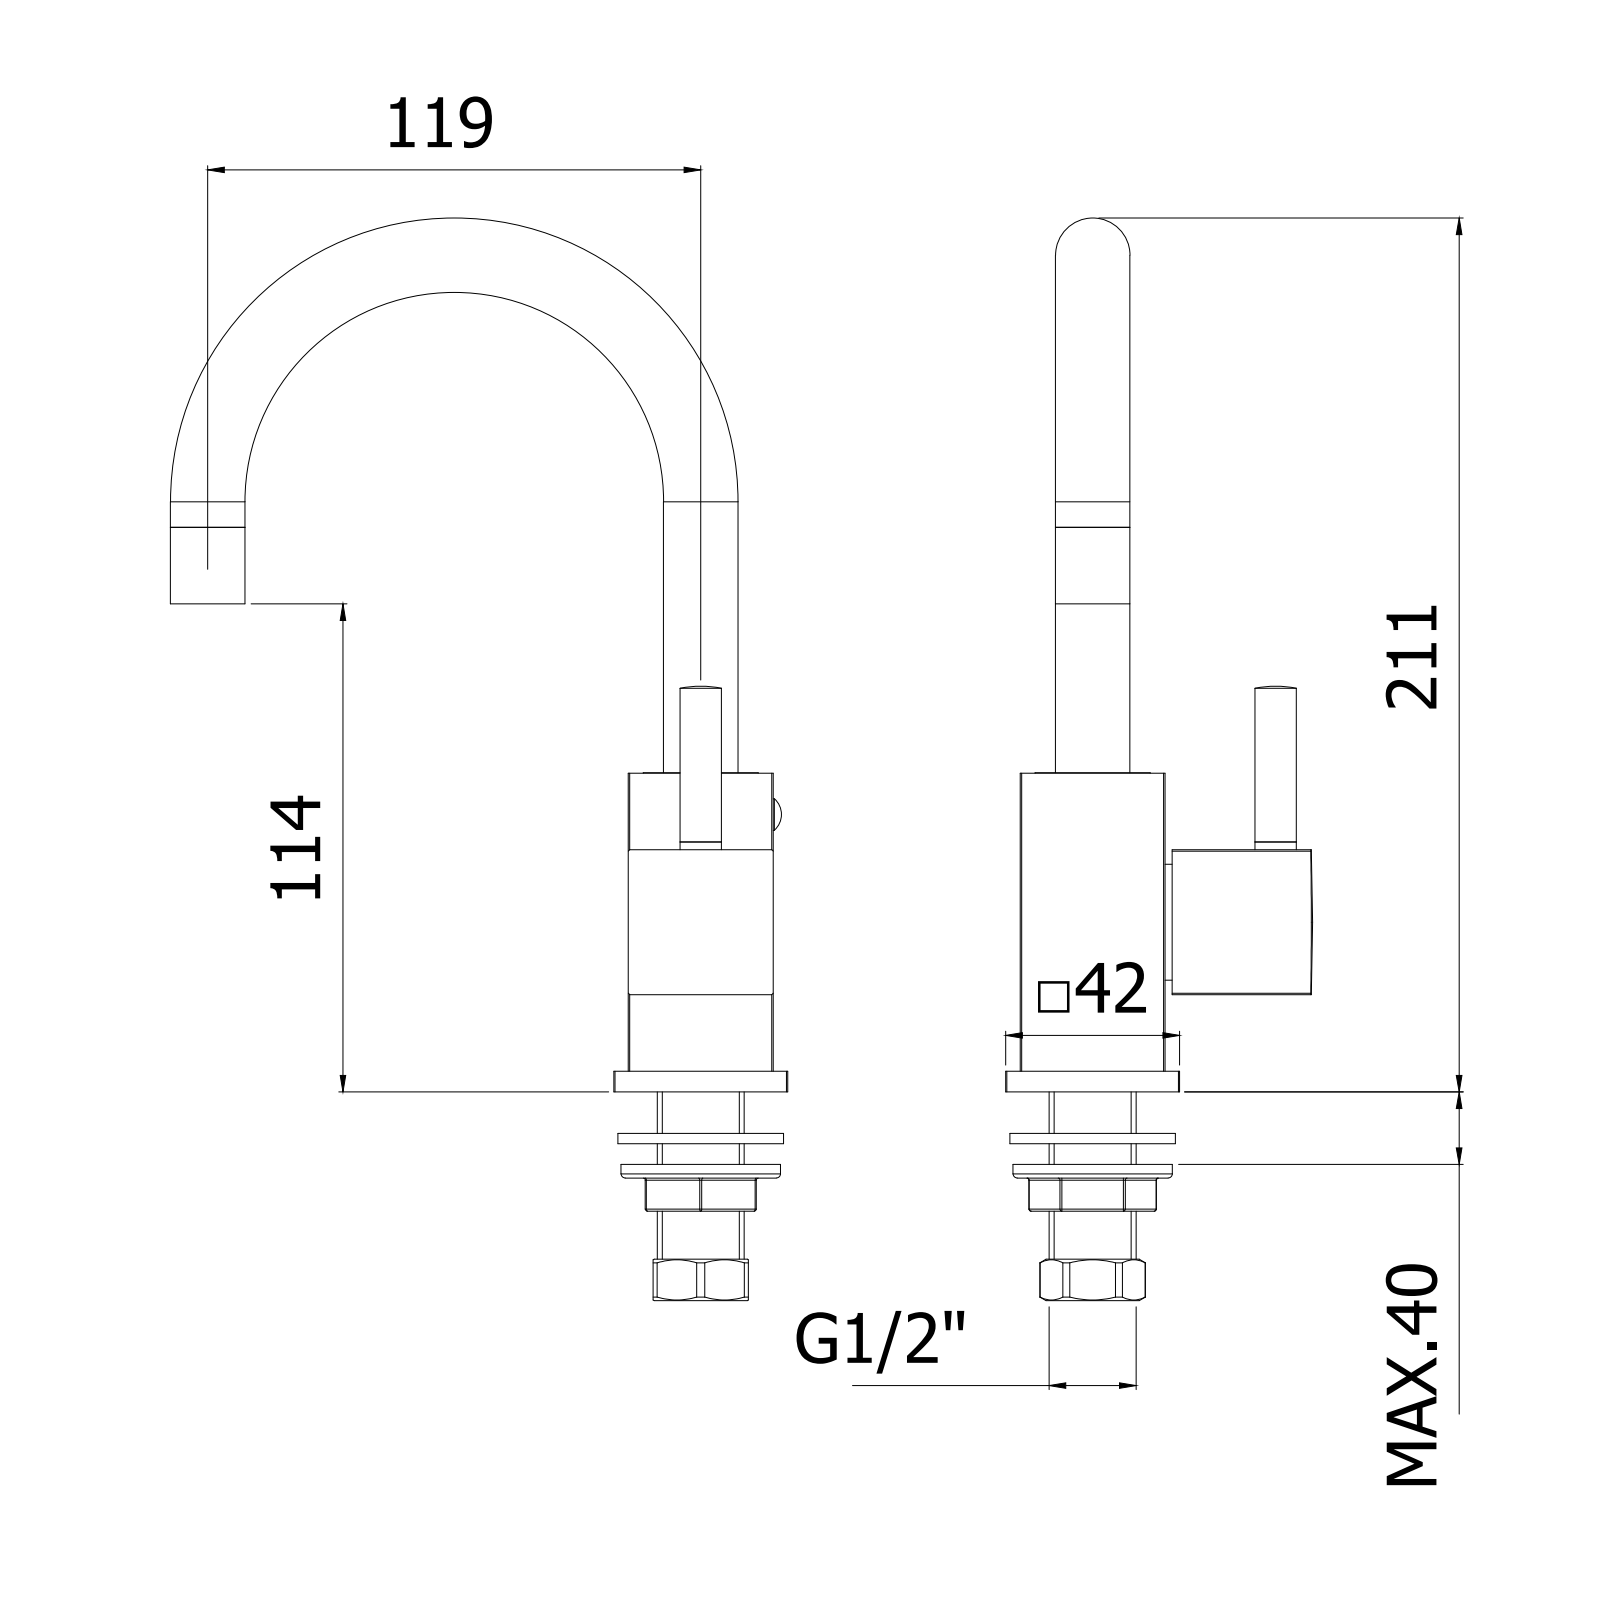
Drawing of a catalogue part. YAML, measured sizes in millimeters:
part_name: "LEA091CR"
step_written_by: "CREO PARAMETRIC BY PTC INC, 2020044 (CONFIG_CONTROL_DESIGN)"
units: millimeters
bodies: {solids: 2, faces: 508, planar: 118, cylindrical: 326, other: 64}
overall_size: [211.1, 149.1, 74.49]
volume: 145388
surface_area: 64763
round_holes:
  - {diameter: 0.5, count: 51}
  - {diameter: 6, count: 2}
  - {diameter: 15, count: 2}
  - {diameter: 22, count: 2}
  - {diameter: 3, count: 1}
  - {diameter: 4, count: 1}
  - {diameter: 4.5, count: 1}
  - {diameter: 5.5, count: 1}
  - {diameter: 9, count: 1}
  - {diameter: 10, count: 1}
  - {diameter: 10.2, count: 1}
  - {diameter: 12, count: 1}
round_bosses_or_shafts:
  - {diameter: 12, count: 2}
  - {diameter: 28, count: 1}
  - {diameter: 27.8, count: 1}
  - {diameter: 23.4, count: 1}
  - {diameter: 18.8, count: 1}
  - {diameter: 18.5, count: 1}
  - {diameter: 18, count: 1}
  - {diameter: 15.7, count: 1}
partial_cylinders:
  - {radius: 24.5, count: 2}
  - {radius: 29.5, count: 1}
face_to_face_distances: [35, 18.5, 53.5, 23.5, 3.5, 58.5, 38.5, 5, 77, 72]
hole_center_spacings: [3.35, 1.5, 2.12, 4.74, 3, 5.4, 4.5, 4.24]
